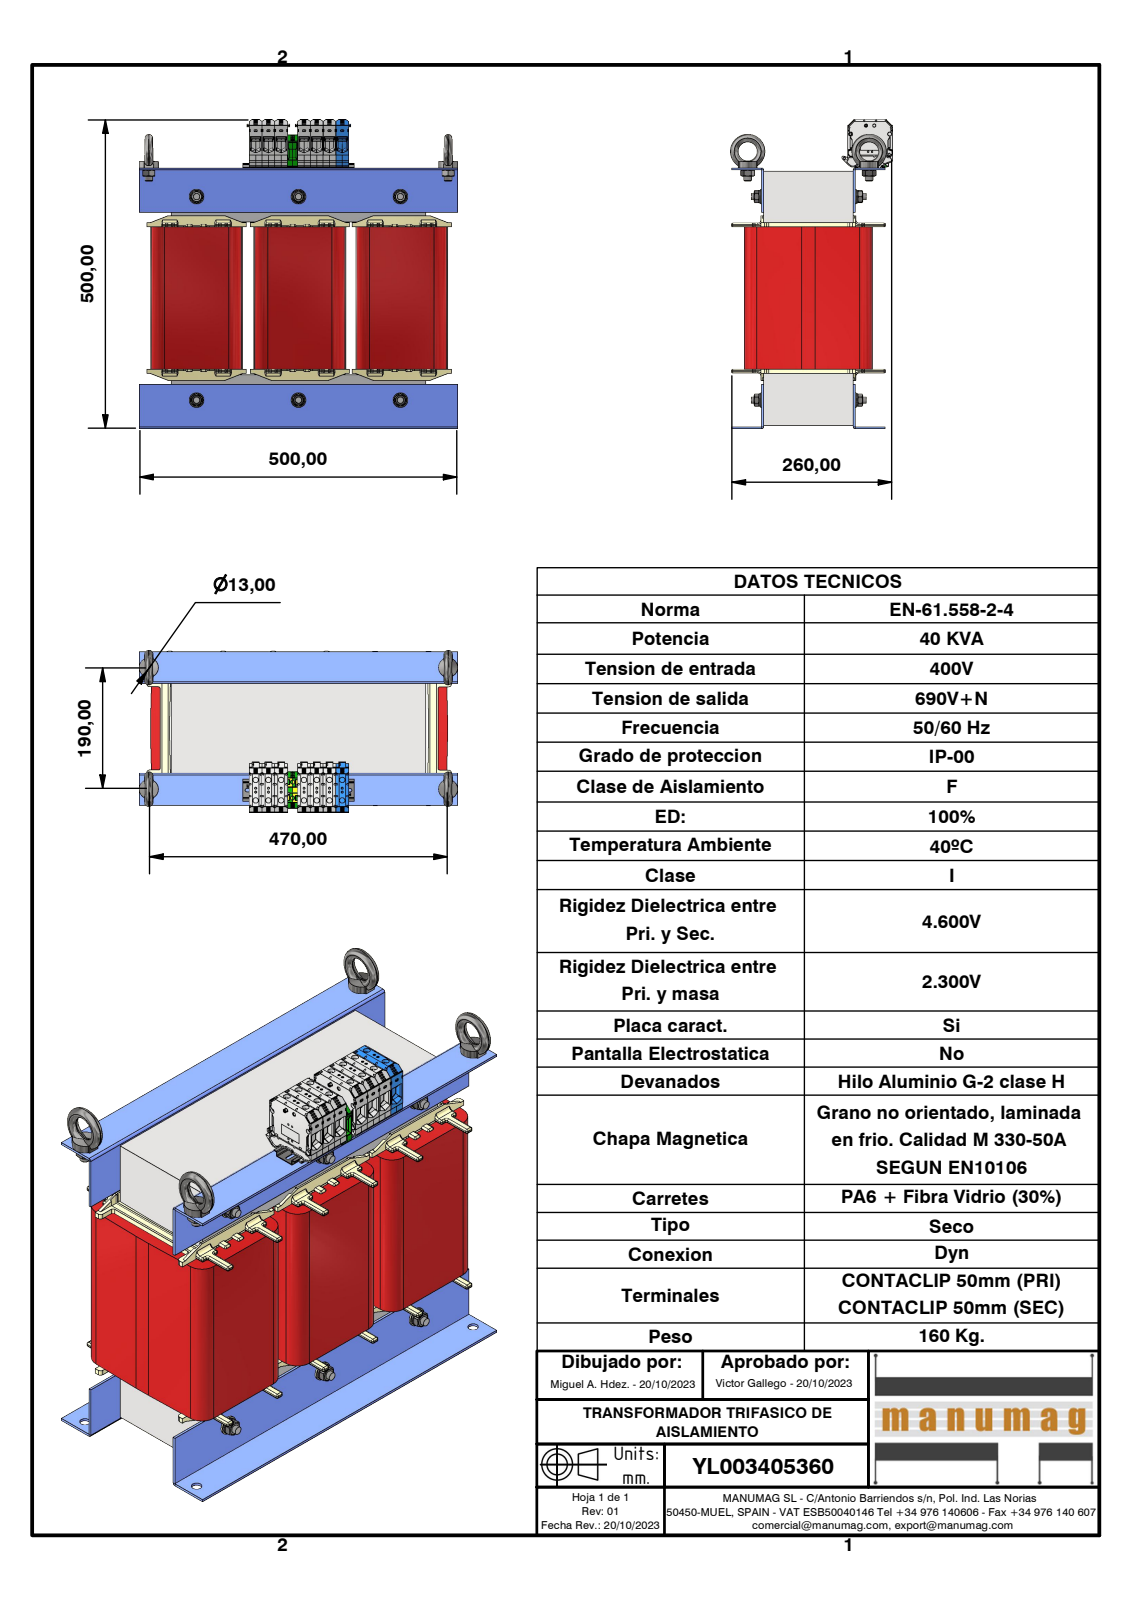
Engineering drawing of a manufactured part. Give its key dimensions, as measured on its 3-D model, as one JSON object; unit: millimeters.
{"part_name": "YL003405360; 3UI240 400 x 400 - 140; UI 240_140_BOBINADO; RC80 NT080 (+8 more)", "step_written_by": "Autodesk Inventor 2023 (AUTOMOTIVE_DESIGN)", "units": "millimeters", "bodies": {"solids": 88, "faces": 13103, "planar": 7552, "cylindrical": 4281, "other": 1270}, "overall_size": [500, 486.7, 253.75], "volume_mm3": 29430000, "surface_area_mm2": 3094000, "round_holes": [[2.75, 14], [2.95, 14], [8.5, 14], [13, 10], [2.5, 8], [8.38, 6], [10, 6], [10.5, 6], [15, 6], [2, 4], [3.4, 4], [6.5, 4]], "round_bosses_or_shafts": [[23, 6], [20, 6], [11.5, 6], [12, 4], [10.8, 4], [54, 2], [4.6, 2]], "partial_cylinders_radius": [[0.3, 451], [2, 277], [1, 266], [0.5, 68], [0.81, 33], [1.9, 32], [0.3, 26], [0.49, 24]], "face_to_face_distances": [5, 3, 140, 162.39, 2, 29.89, 80, 160, 143, 145.2], "hole_center_spacings": [20, 23.85, 27.59, 13, 19, 20.88, 40, 42.06]}
